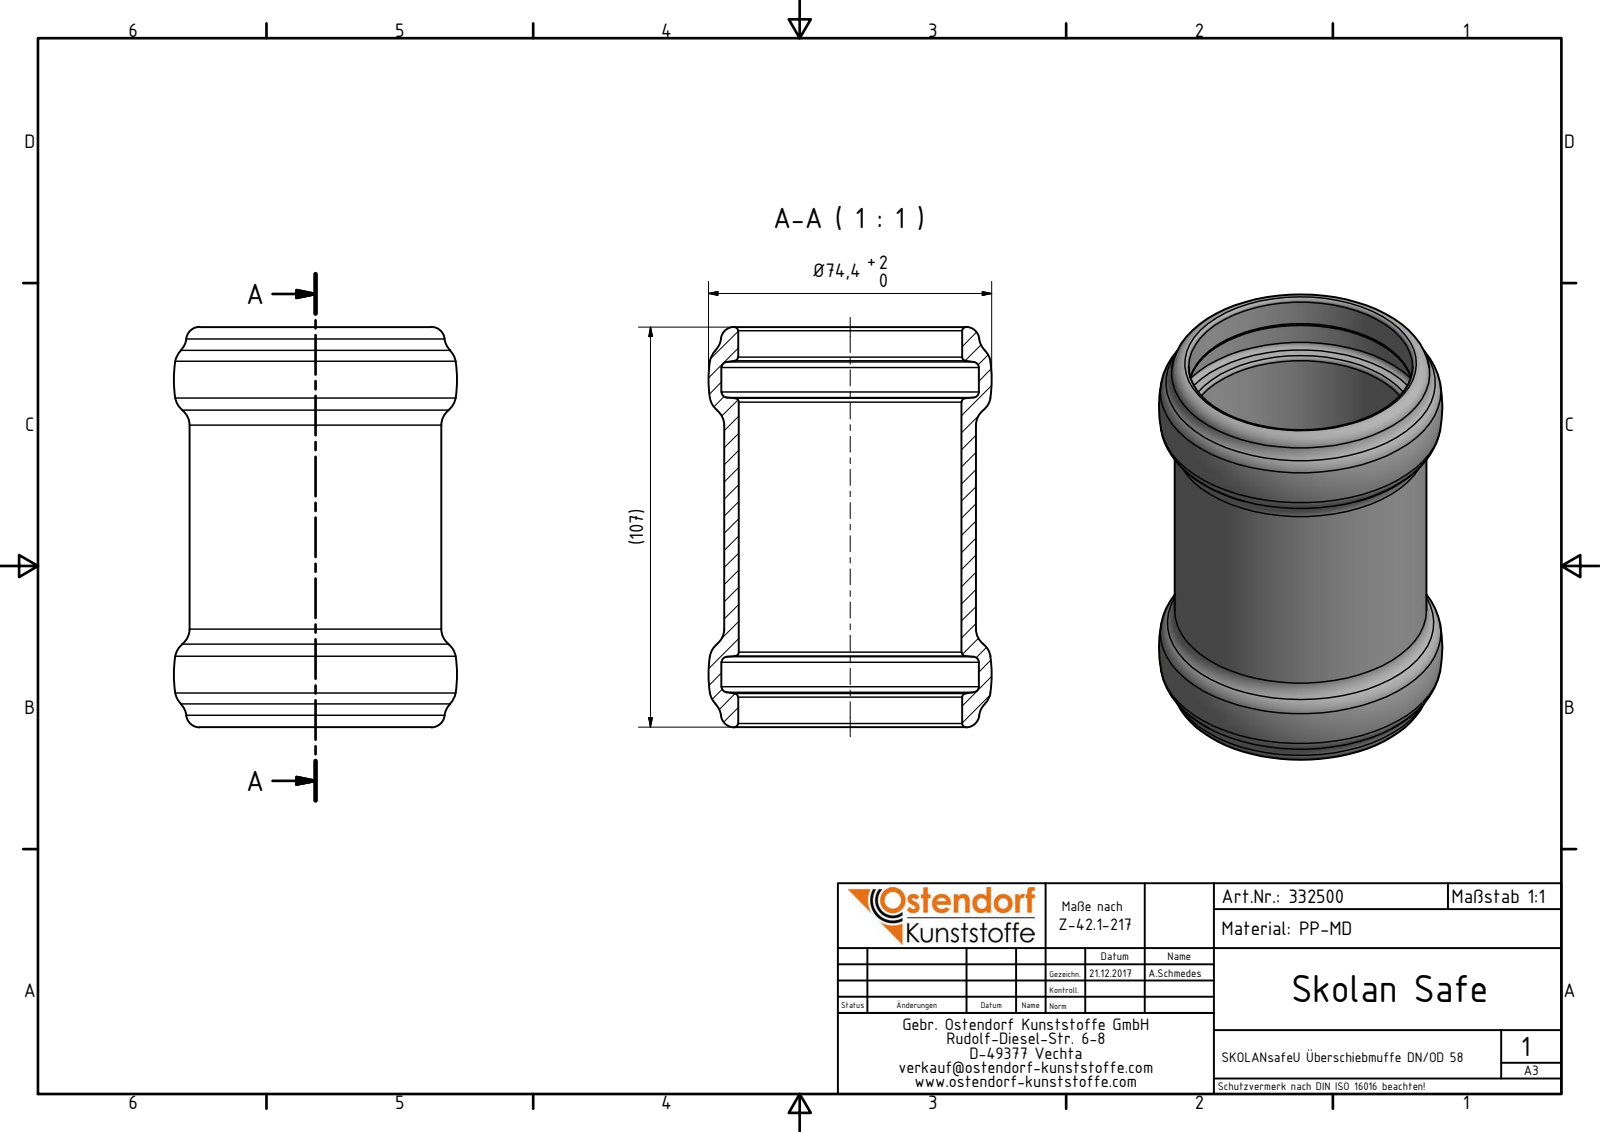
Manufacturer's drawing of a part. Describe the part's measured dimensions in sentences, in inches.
The part is named "332500 SKOLANsafeU Überschiebmuffe DN_OD 58". Its 3-D file was written by "Autodesk Inventor 2016 (AUTOMOTIVE_DESIGN)". It is 1 solid with 32 faces: 0 planar, 6 cylindrical and 26 other. Overall it measures 4.134 by 2.929 by 2.929 inches. Its volume is 5.415 cubic inches and its surface area 72.73 square inches. Round holes: 1 of diameter 2.303, 1 of diameter 2.315, 1 of diameter 2.661. Round bosses or shafts: 1 of diameter 2.602.
